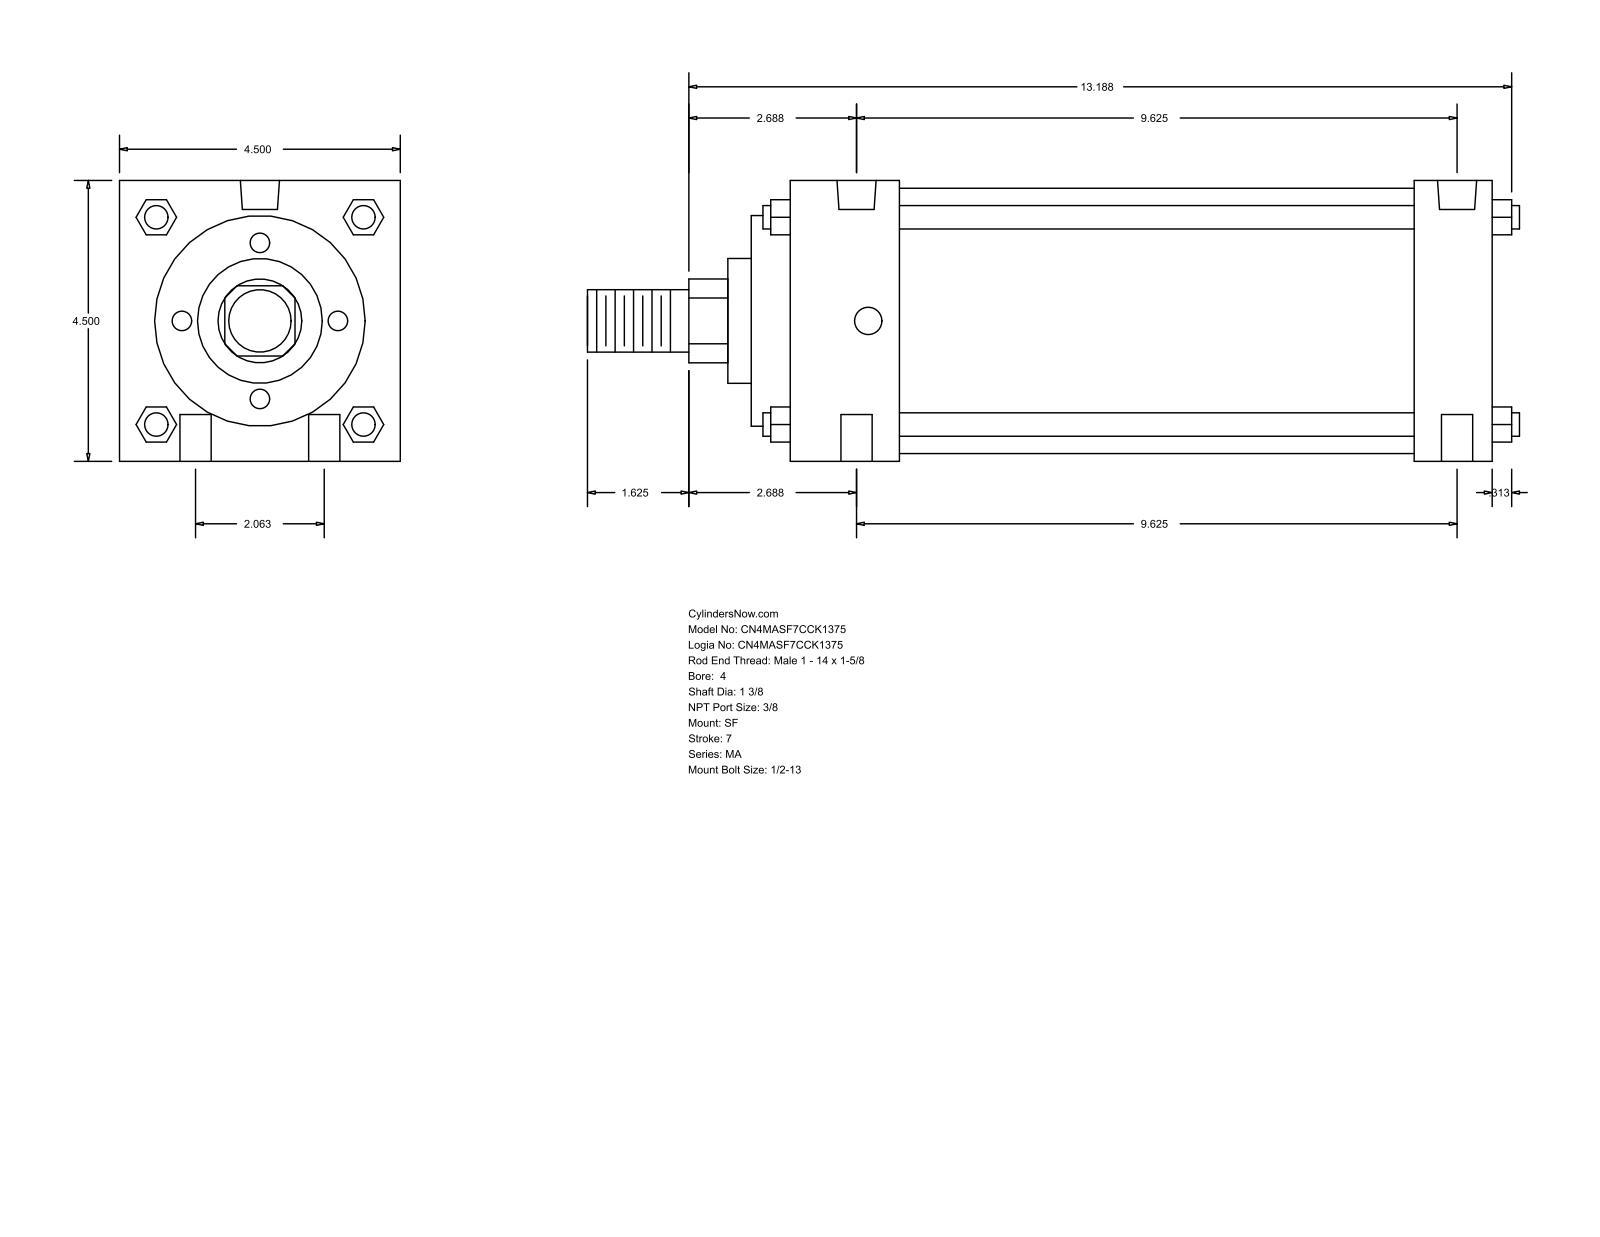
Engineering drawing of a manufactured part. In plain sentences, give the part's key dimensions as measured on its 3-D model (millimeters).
The part is named "MA_SF__0400_1.375". Its 3-D file was written by "GSSL Pune (CONFIG_CONTROL_DESIGN)". It is 0 solids with 126 faces: 95 planar, 31 cylindrical and 0 other. Overall it measures 379.41 by 114.3 by 114.3 millimeters. Round holes: 4 of diameter 12.7, 2 of diameter 11.11, 2 of diameter 15.93. Round bosses or shafts: 4 of diameter 9.53, 1 of diameter 107.95, 1 of diameter 85.72, 1 of diameter 50.8, 1 of diameter 34.92, 1 of diameter 25.4. Partial cylindrical surfaces (rounded edges, fillets, slot ends): 1 of radius 17.06. The main face-to-face distances are 114.3, 285.75, 301.62, 15.87, 269.87, 254, 31.75, 60.32, 44.45, 209.55. The hole center spacings are 26.19, 245.88, 244.48, 52.38, 250.03, 234.95.
